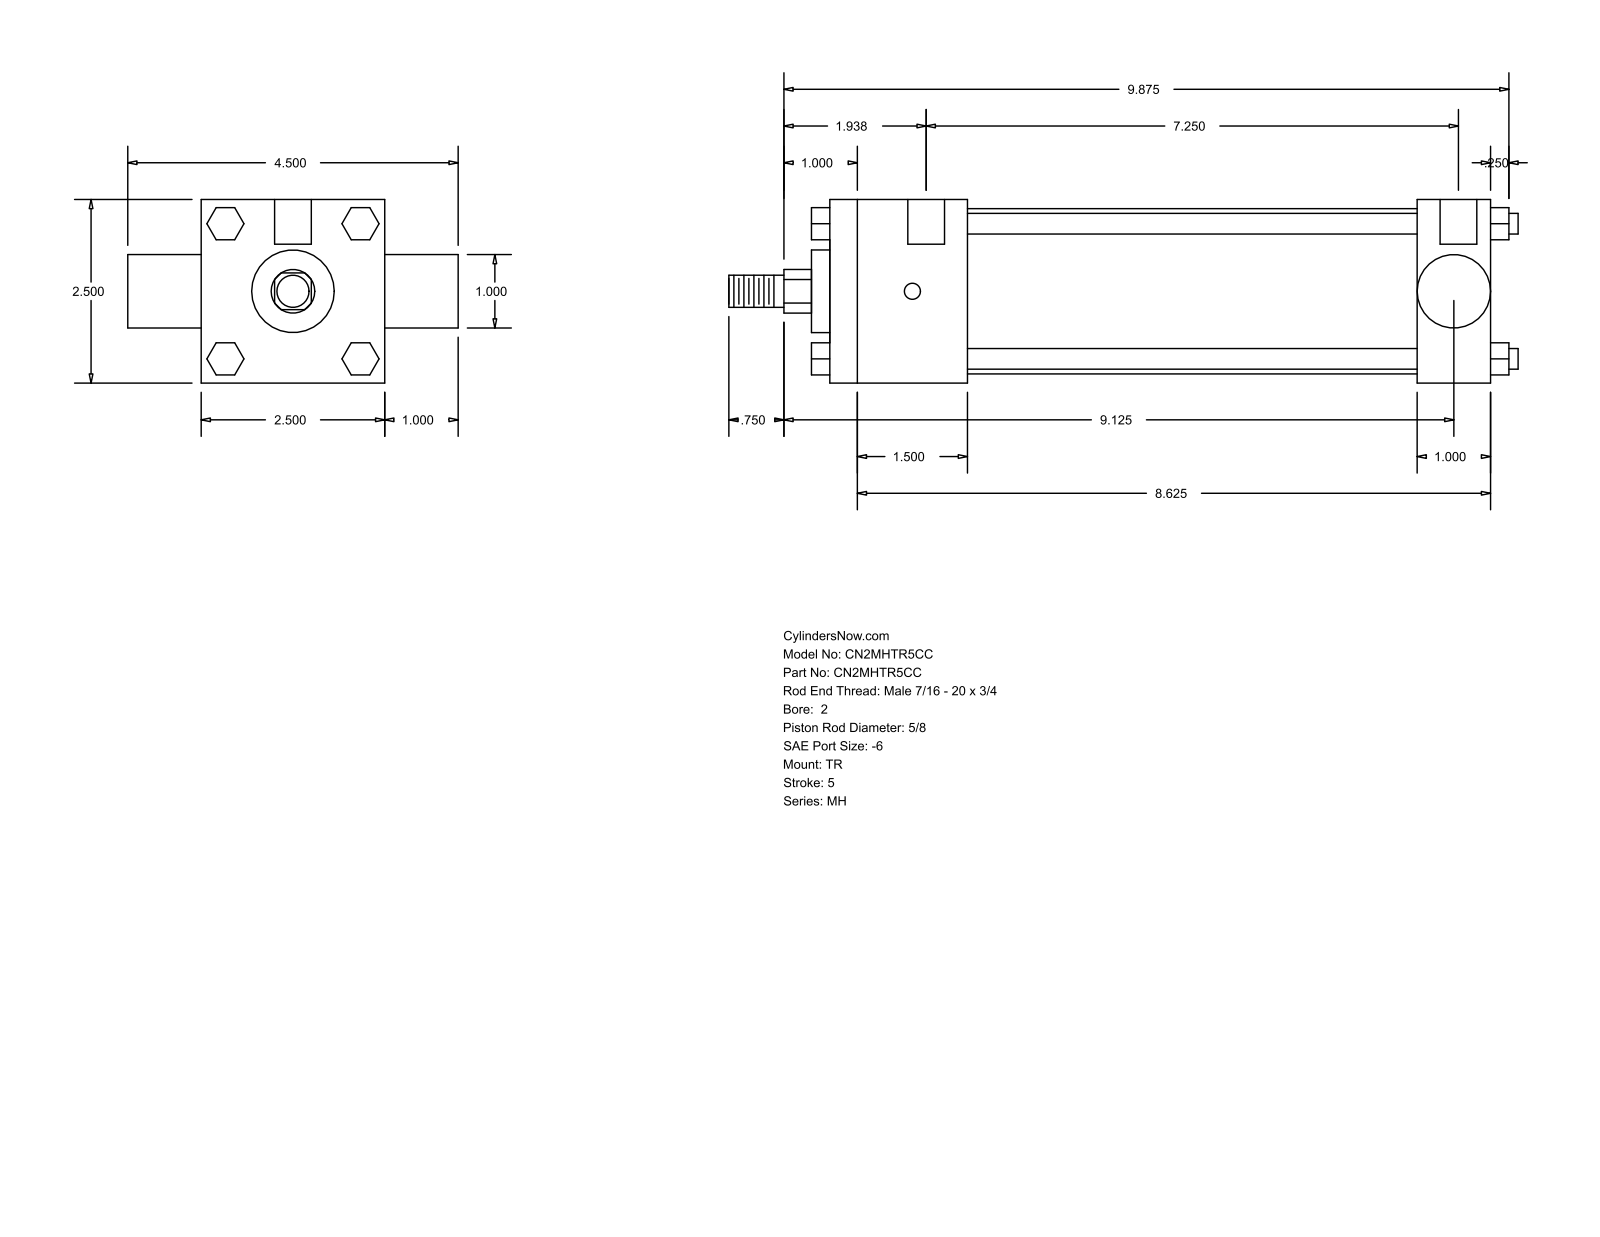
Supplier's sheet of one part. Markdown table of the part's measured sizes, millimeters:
| quantity | value |
| --- | --- |
| part name | MH_TR__0200_0.625 |
| STEP written by | GSSL Pune (CONFIG_CONTROL_DESIGN) |
| units | millimeters |
| bodies | 0 solids, 120 faces (92 planar, 28 cylindrical, 0 other) |
| overall size | 273.05 × 114.3 × 63.5 |
| round holes (diameter × count) | 5.56 × 3, 12.7 × 2 |
| round bosses / shafts (diameter × count) | 7.14 × 4, 57.15 × 1, 28.57 × 1, 25.35 × 1, 15.88 × 1, 11.11 × 1 |
| partial cylindrical surfaces (radius × count) | 7.54 × 1 |
| main face-to-face distances | 63.5, 228.59, 25.4, 47.62, 203.19, 155.57, 180.97, 6.35, 88.9, 234.94 |
| hole center spacings | 3.18, 4.76, 184.15, 187.33, 188.91, 192.09 |
